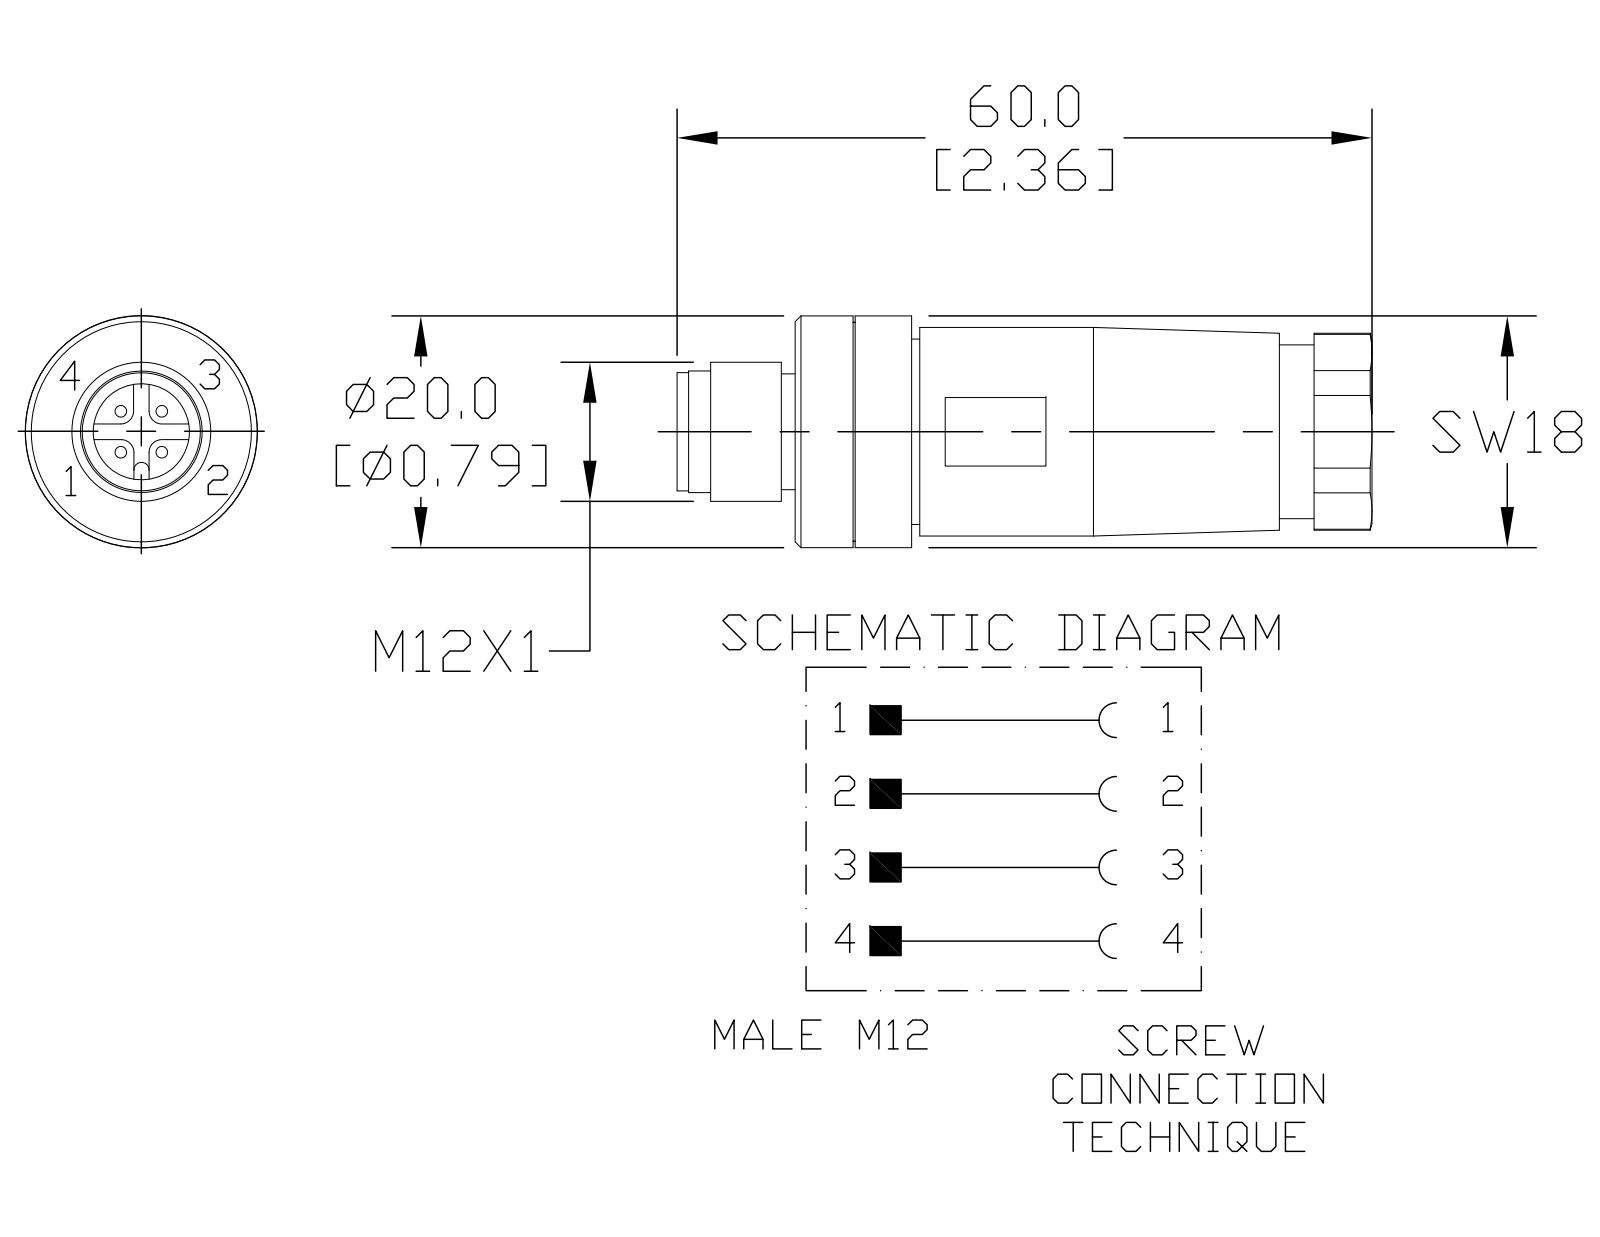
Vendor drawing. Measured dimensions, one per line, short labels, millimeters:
name: 7000-12701-0000000
written by: SolidWorks 2015 (AUTOMOTIVE_DESIGN)
unit: mm
bodies: 1 solid, 807 faces (399 planar, 217 cylindrical, 191 other)
size: 60 × 20 × 19.99
volume: 10 869 mm³; area: 5 376 mm²
holes: 1× ⌀6.98, 1× ⌀8.25
bosses: 3× ⌀1, 1× ⌀17.78, 1× ⌀11.07, 1× ⌀10.66, 1× ⌀9.09, 1× ⌀8.95, 1× ⌀1.03
rounds: 1× R0.62, 1× R10
face distances: 4.91, 2.25, 14.25, 12, 4.84, 44.93, 45, 49.84, 13.84, 16.5
